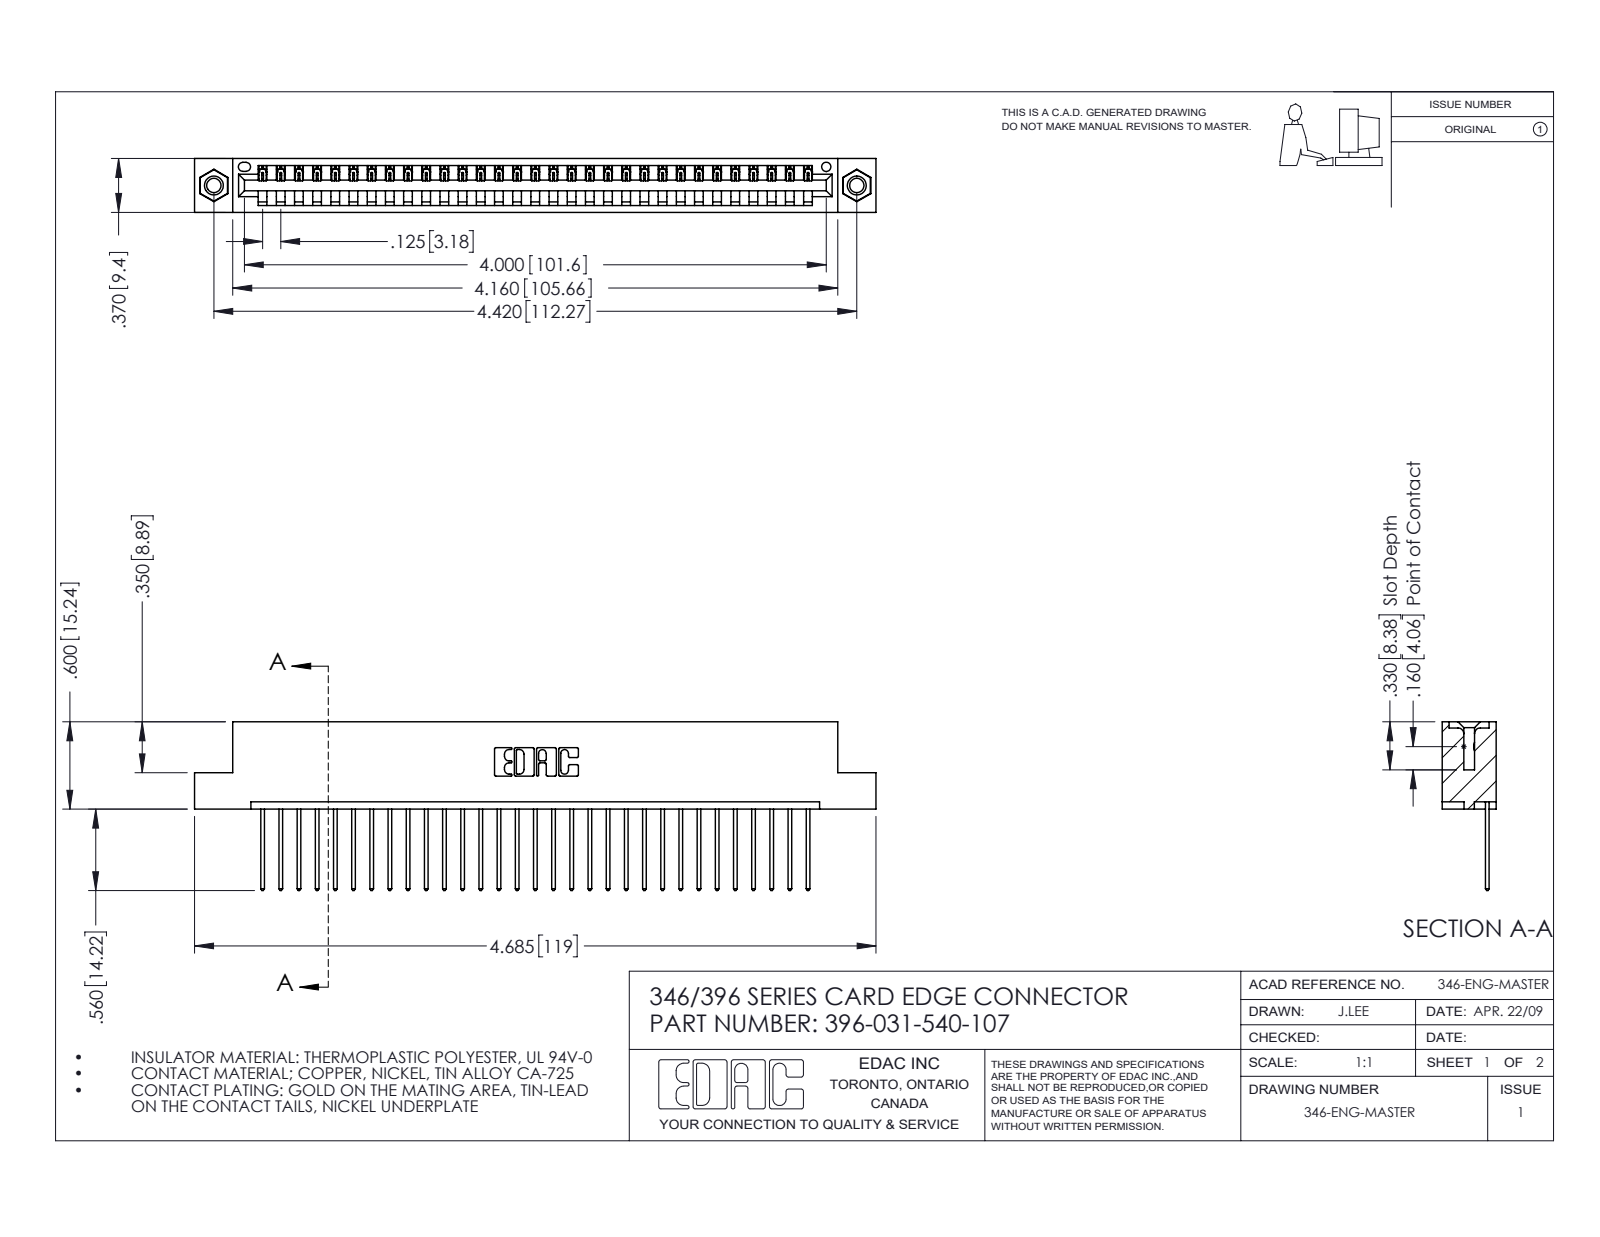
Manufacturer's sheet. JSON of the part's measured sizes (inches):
{"part_name": "346 Part_Flush Mounting Lugs - 0.156 Dia-TI; 345-292-001_345-293-140; 396-031-540-107; 345-250-001_345-250-005-103", "step_written_by": "SolidWorks 2016 (CONFIG_CONTROL_DESIGN)", "units": "inches", "bodies": {"solids": 34, "faces": 1980, "planar": 1348, "cylindrical": 616, "other": 16}, "overall_size": [4.685, 1.16, 0.37], "volume_in3": 0.692, "surface_area_in2": 22.32, "round_holes": [[0.098, 2], [0.125, 2], [0.156, 2], [0.064, 1]], "round_bosses_or_shafts": [[0.155, 2]], "partial_cylinders_radius": [[0.006, 62], [0.01, 62], [0.01, 22], [0.007, 6], [0.031, 6], [0.026, 3], [0.031, 2], [0.04, 2]], "face_to_face_distances": [0.048, 0.322, 0.37, 0.25, 0.072, 0.298, 0.025, 0.148, 0.222, 0.1], "hole_center_spacings": [0.246, 4.212, 4.42]}
